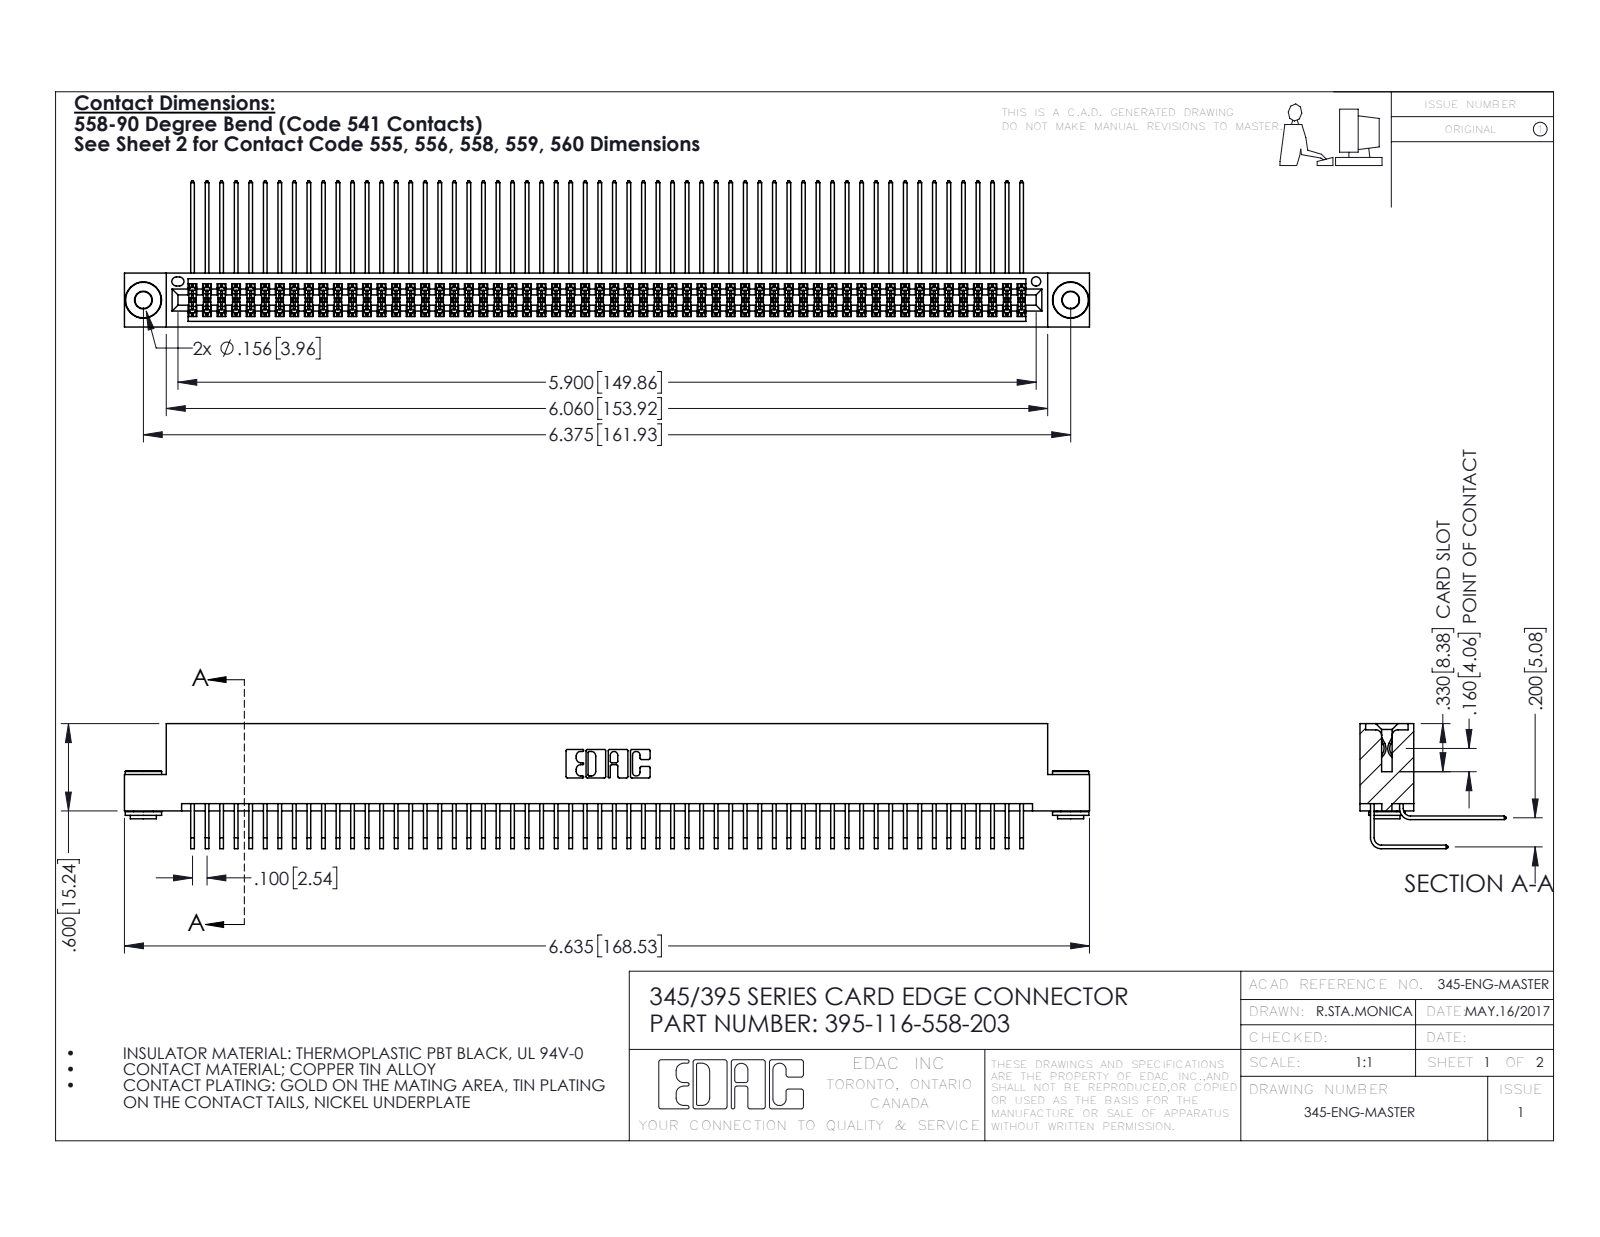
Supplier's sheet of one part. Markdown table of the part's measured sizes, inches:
| quantity | value |
| --- | --- |
| part name | 345-250-002_345-250-002-102; 345-292-001_558 559 Tail - 1; 395-116-558-203; 345-292-001_558 Tail - 2 (+1 more) |
| STEP written by | SolidWorks 2016 (CONFIG_CONTROL_DESIGN) |
| units | inches |
| bodies | 119 solids, 6196 faces (4150 planar, 2038 cylindrical, 8 other) |
| overall size | 6.635 × 1.005 × 0.859 |
| volume | 1.05 in³ |
| surface area | 45.1 in² |
| round holes (diameter × count) | 0.116 × 2, 0.156 × 2, 0.064 × 1 |
| round bosses / shafts (diameter × count) | 0.25 × 2, 0.18 × 2, 0.136 × 2 |
| partial cylindrical surfaces (radius × count) | 0.006 × 174, 0.01 × 22, 0.007 × 6, 0.031 × 6, 0.026 × 3, 0.014 × 2, 0.019 × 2, 0.022 × 2 |
| main face-to-face distances | 0.072, 0.298, 0.2, 0.37, 0.025, 0.098, 0.272, 0.225, 0.025, 0.175 |
| hole center spacings | 0.27, 6.139, 6.375 |
